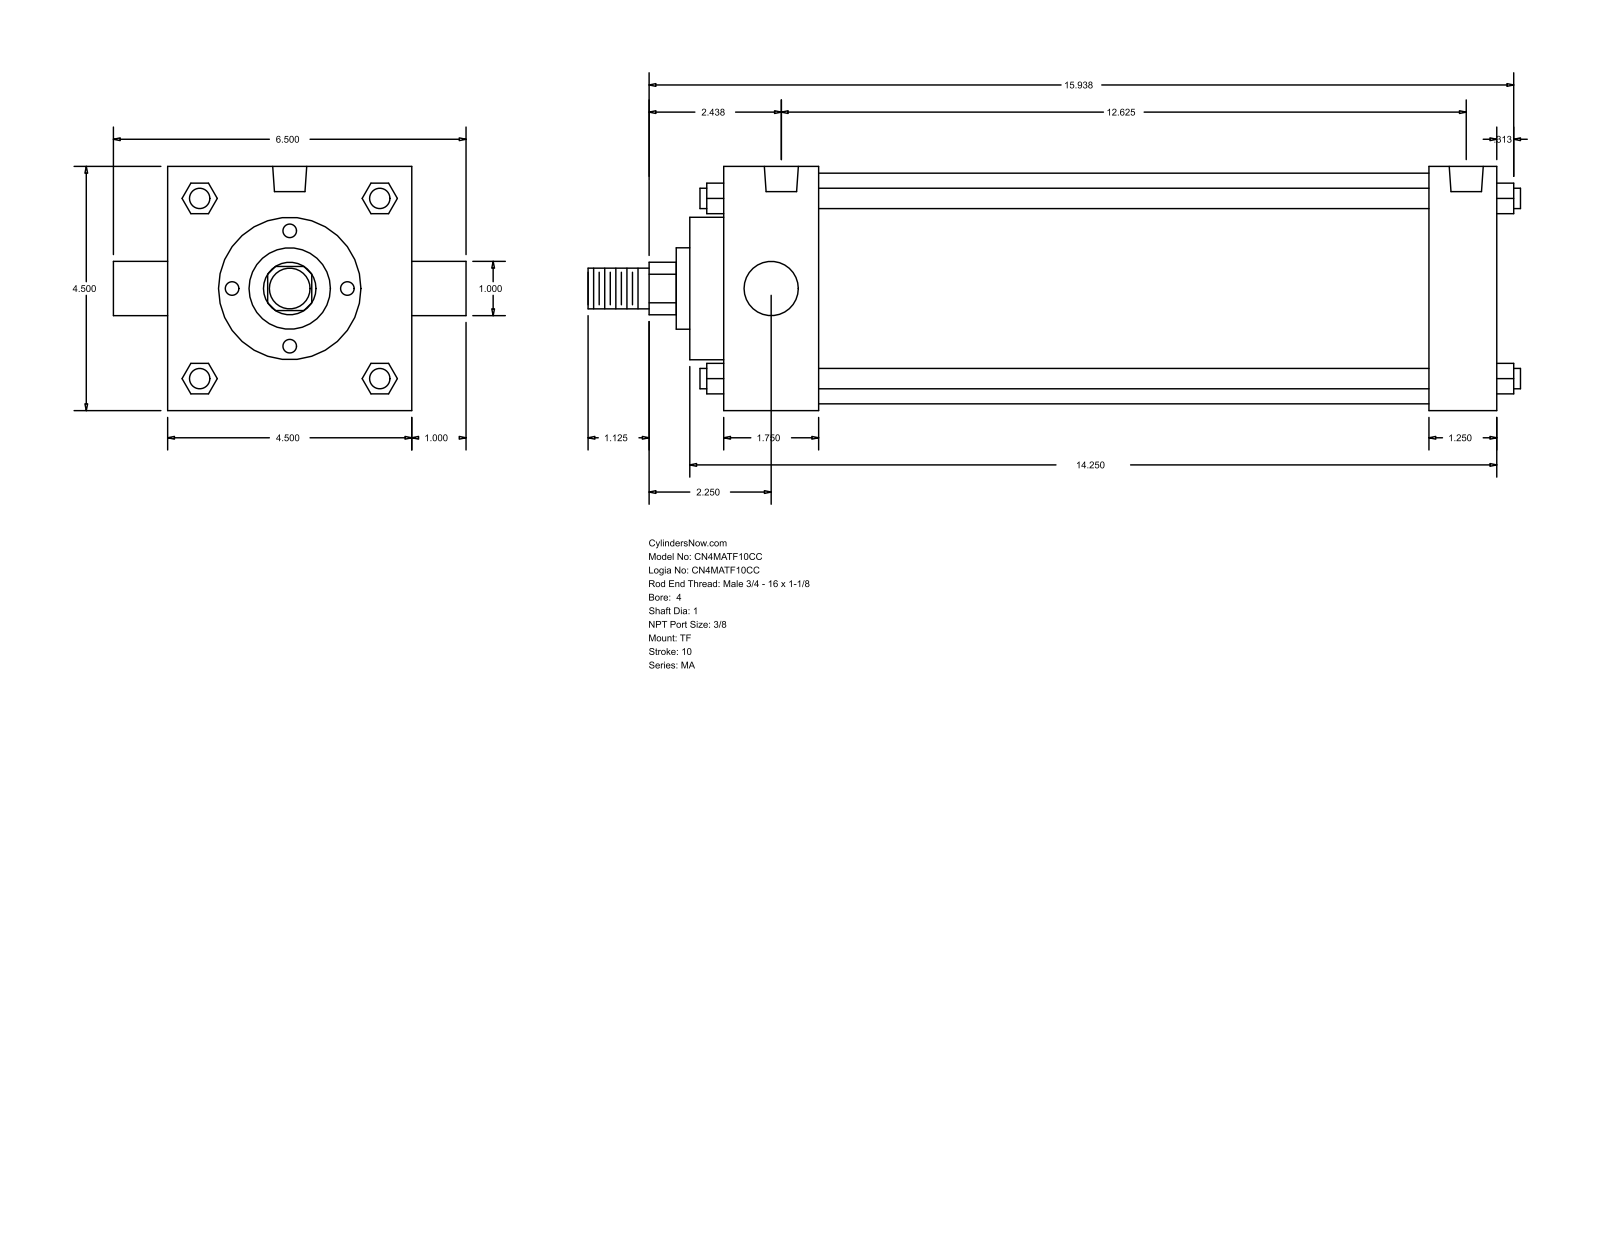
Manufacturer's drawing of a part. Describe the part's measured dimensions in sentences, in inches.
The part is named "MA_TF__0400_1". Its 3-D file was written by "GSSL Pune (CONFIG_CONTROL_DESIGN)". It is 0 solids with 122 faces: 93 planar, 29 cylindrical and 0 other. Overall it measures 17.187 by 6.5 by 4.5 inches. Round holes: 3 of diameter 0.437, 2 of diameter 0.627. Round bosses or shafts: 4 of diameter 0.375, 2 of diameter 1, 1 of diameter 4.25, 1 of diameter 2.625, 1 of diameter 1.5, 1 of diameter 0.75. Partial cylindrical surfaces (rounded edges, fillets, slot ends): 1 of radius 0.484. The main face-to-face distances are 4.5, 14.25, 13, 1.25, 1.75, 11.25, 12.5, 0.625, 2.375, 13.625. The hole center spacings are 0.187, 0.188, 12.25, 12.437, 12.438, 12.625.
